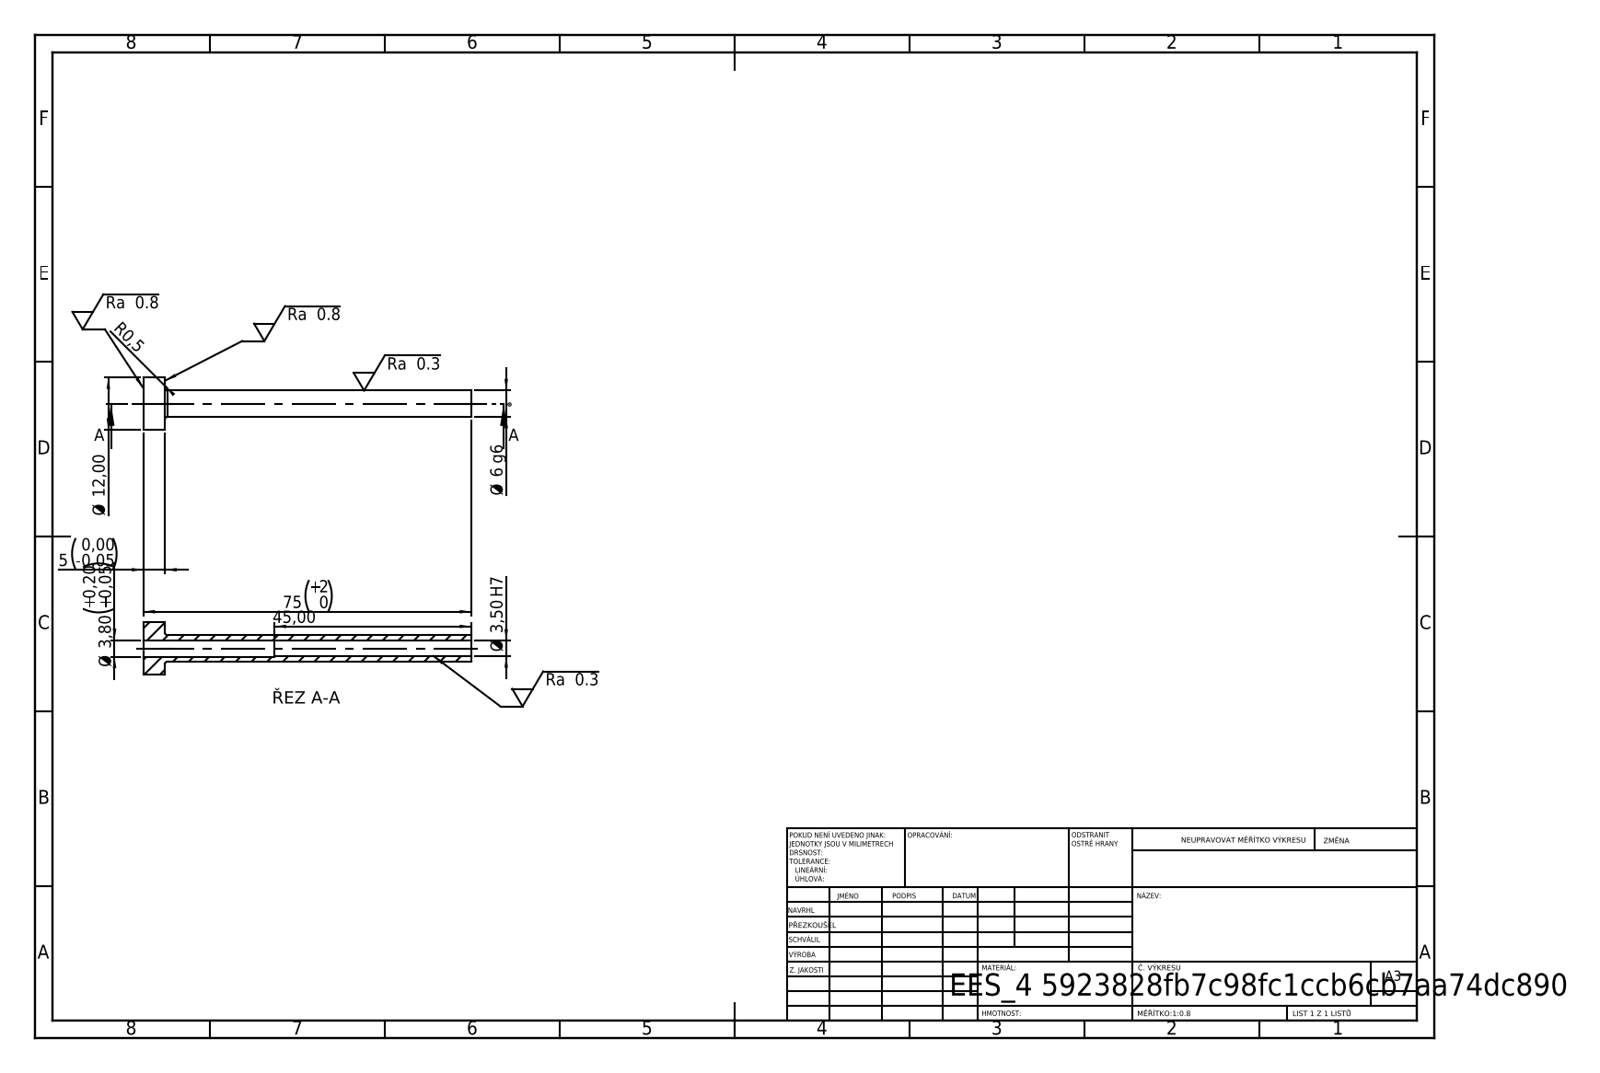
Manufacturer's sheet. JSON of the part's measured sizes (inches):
{"step_written_by": "SolidWorks 2019 (CONFIG_CONTROL_DESIGN)", "units": "inches", "bodies": {"solids": 1, "faces": 14, "planar": 4, "cylindrical": 8, "other": 2}, "overall_size": [2.953, 0.472, 0.472], "volume_in3": 0.108, "surface_area_in2": 3.974, "round_holes": [[0.138, 1], [0.15, 1]], "round_bosses_or_shafts": [[0.472, 1], [0.236, 1]], "face_to_face_distances": [0.197, 2.953, 2.756, 1.181, 0.984, 1.772]}
